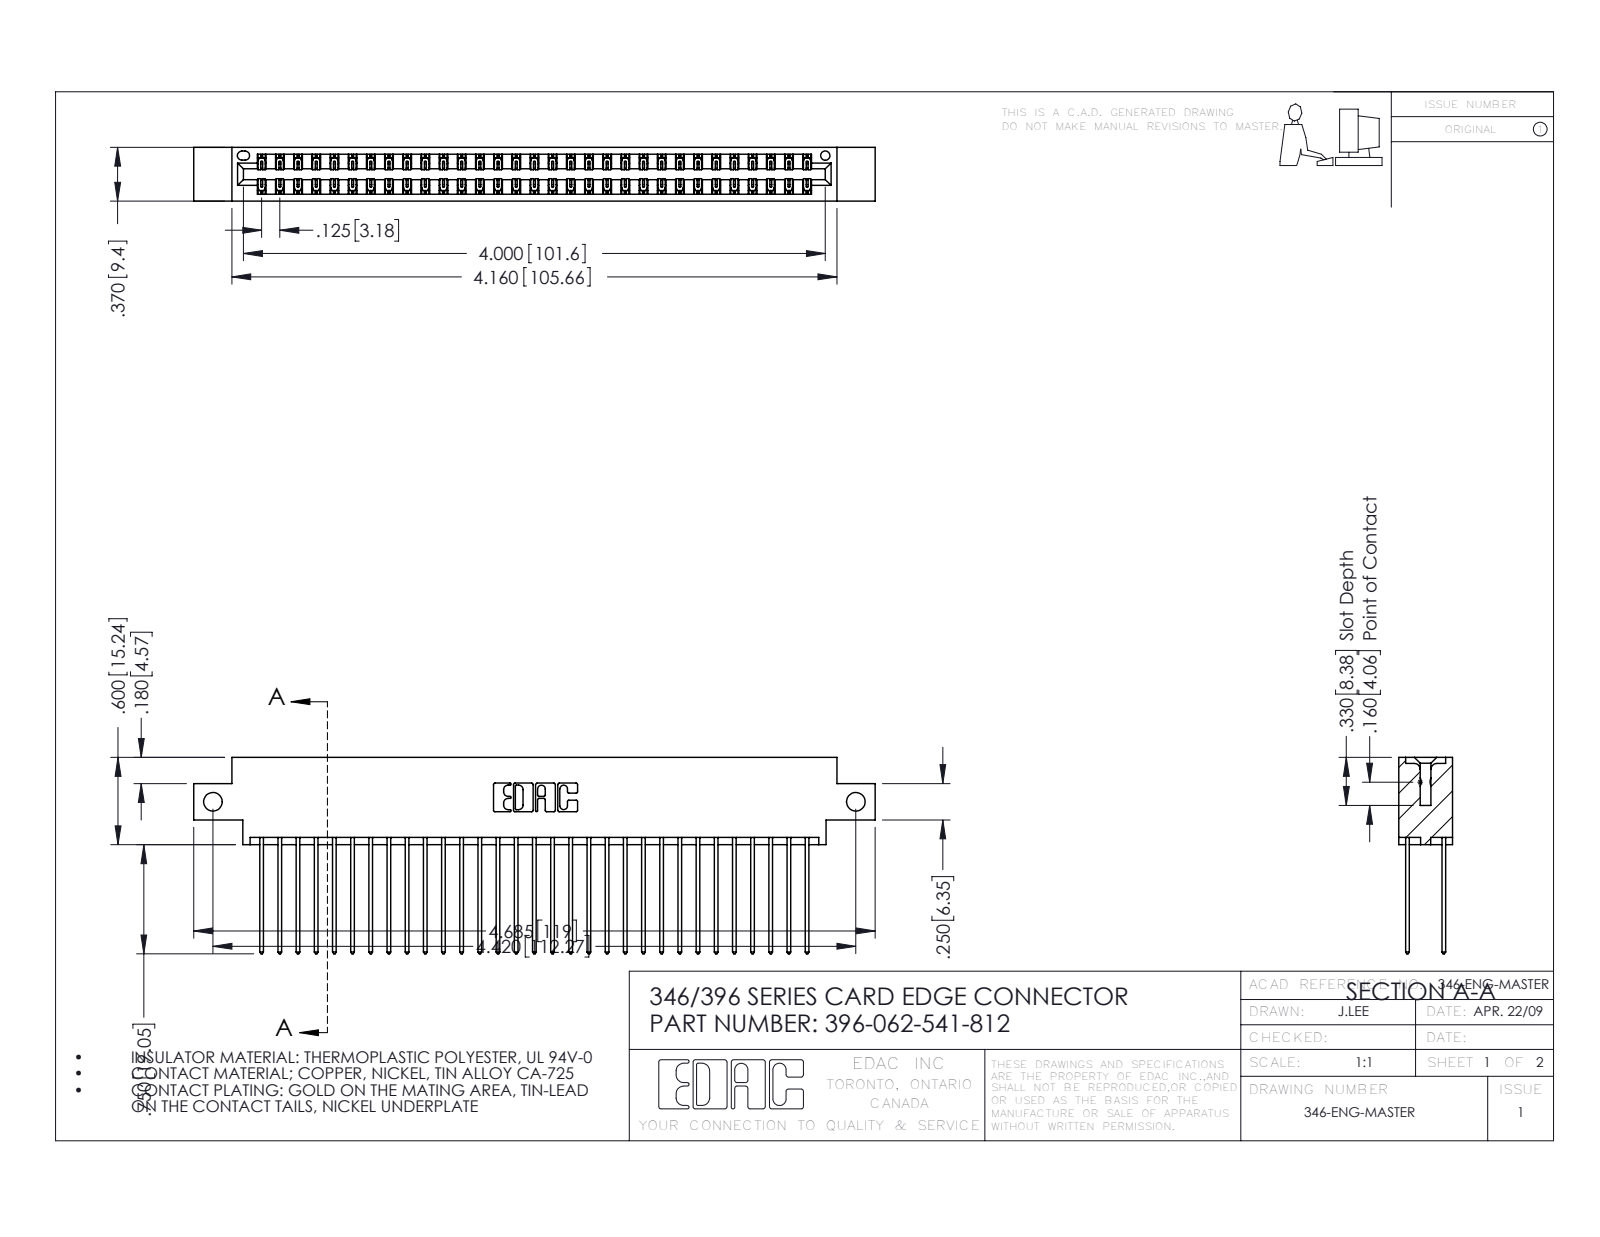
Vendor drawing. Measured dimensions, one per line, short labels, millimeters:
name: 396-062-541-812; 345-292-001_345-293-141; 346 Part_0.170 Offset - Side Mount
written by: SolidWorks 2016 (CONFIG_CONTROL_DESIGN)
unit: mm
bodies: 63 solids, 3350 faces (2250 planar, 1100 cylindrical, 0 other)
size: 119 × 34.3 × 9.4
volume: 11 600 mm³; area: 17 560 mm²
holes: 2× ⌀3.3, 1× ⌀1.6
rounds: 93× R0.2, 62× R0.3, 22× R0.3, 6× R0.2, 6× R0.8, 3× R0.7, 2× R0.4, 2× R0.6
face distances: 1.2, 8.2, 6.4, 1.8, 7.6, 0.6, 9.4, 7, 5.7, 3.8
hole spacings: 112.3
